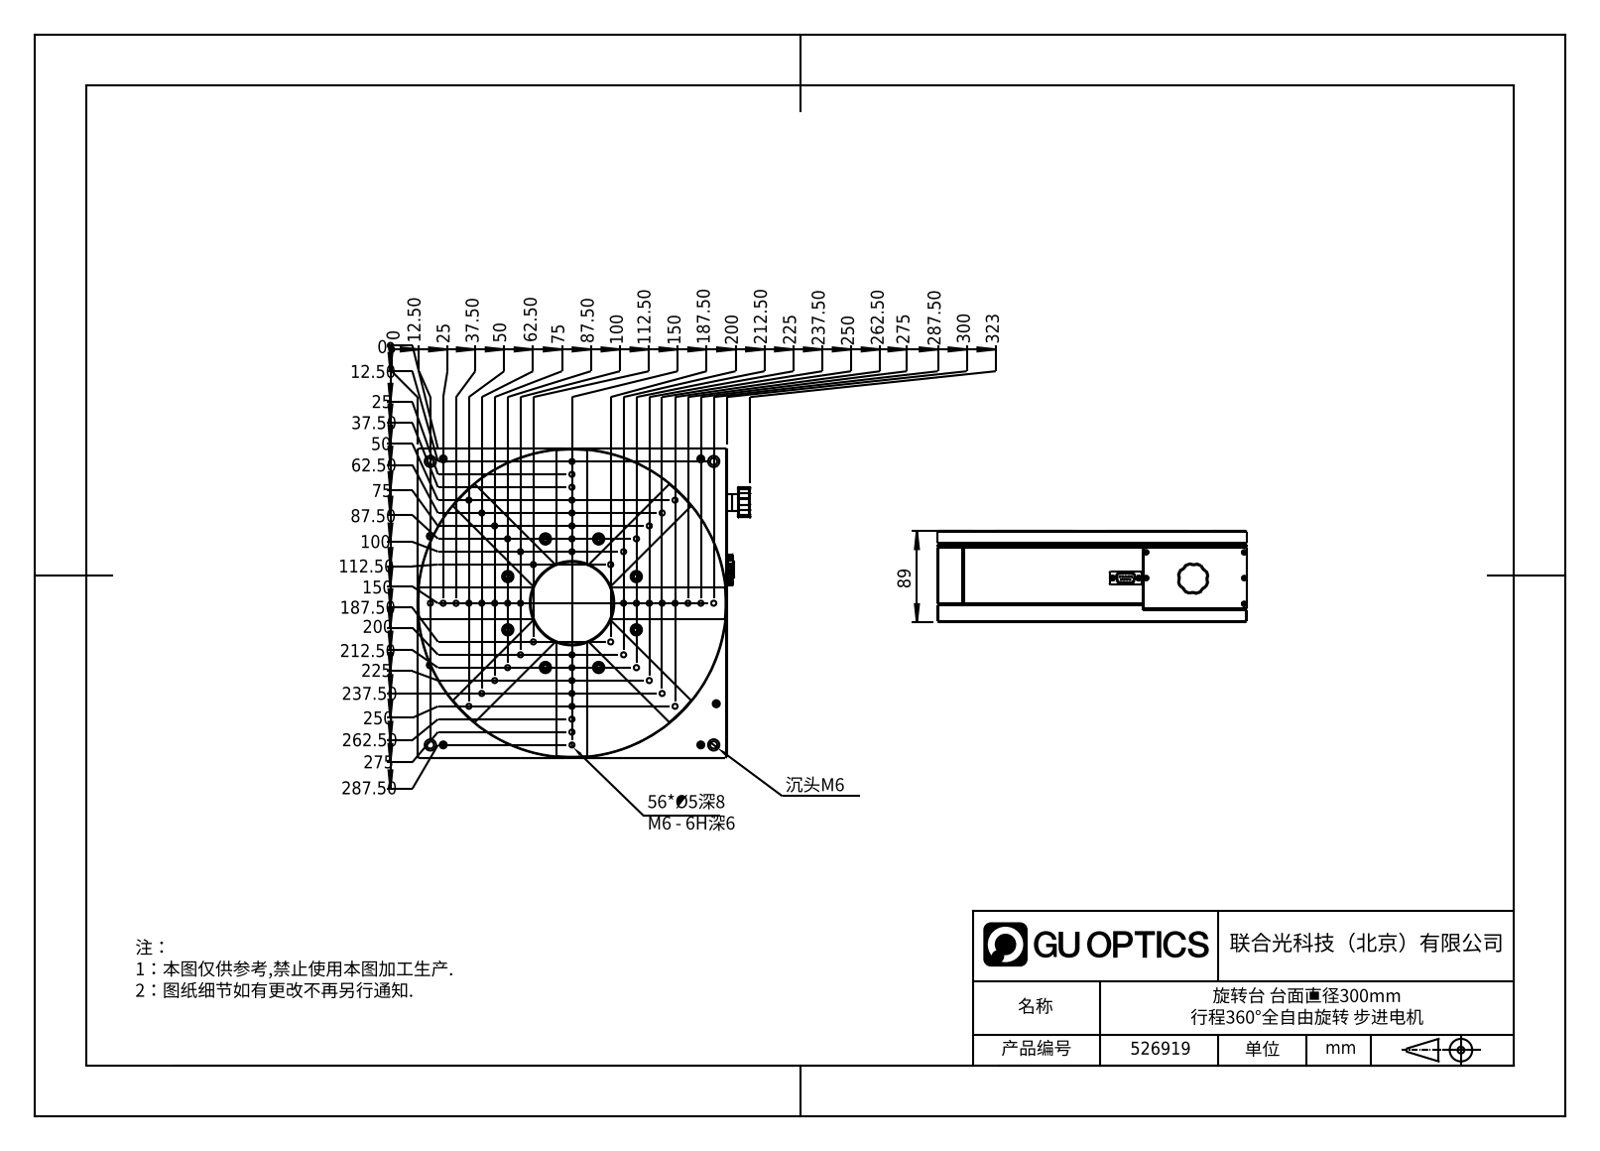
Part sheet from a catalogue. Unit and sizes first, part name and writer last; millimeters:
Units: millimetres
Overall size (bounding box): 395.5 × 338.5 × 65
Round holes (diameter × count): ⌀5 ×24, ⌀5.1 ×4, ⌀7 ×3, ⌀6.5 ×1, ⌀11 ×1, ⌀24 ×1, ⌀180 ×1
Round bosses / shafts (diameter × count): ⌀1 ×6, ⌀300 ×1, ⌀40 ×1, ⌀38 ×1, ⌀20 ×1, ⌀16 ×1, ⌀8 ×1, ⌀6.35 ×1
Partial cylindrical surfaces — rounded edges, fillets, slot ends (radius × count): R2 ×14, R1.9 ×8, R5 ×4, R5.1 ×4, R40 ×3, R30 ×2, R20 ×1
Main face-to-face distances: 49.5, 15.5, 10, 5.5, 55, 65, 303, 319.5, 8, 34
Hole centre spacings: 176.78, 25, 201.56, 230.49, 35.36, 152.07, 175, 55.9
Volume: 3 872 000 mm³ · Surface area: 370 053 mm²
Bodies: 3 solids, 325 faces (143 planar, 170 cylindrical, 12 other)
Part name (STEP PRODUCT): FMSR300
STEP written by: SolidWorks 2017 (AUTOMOTIVE_DESIGN)
